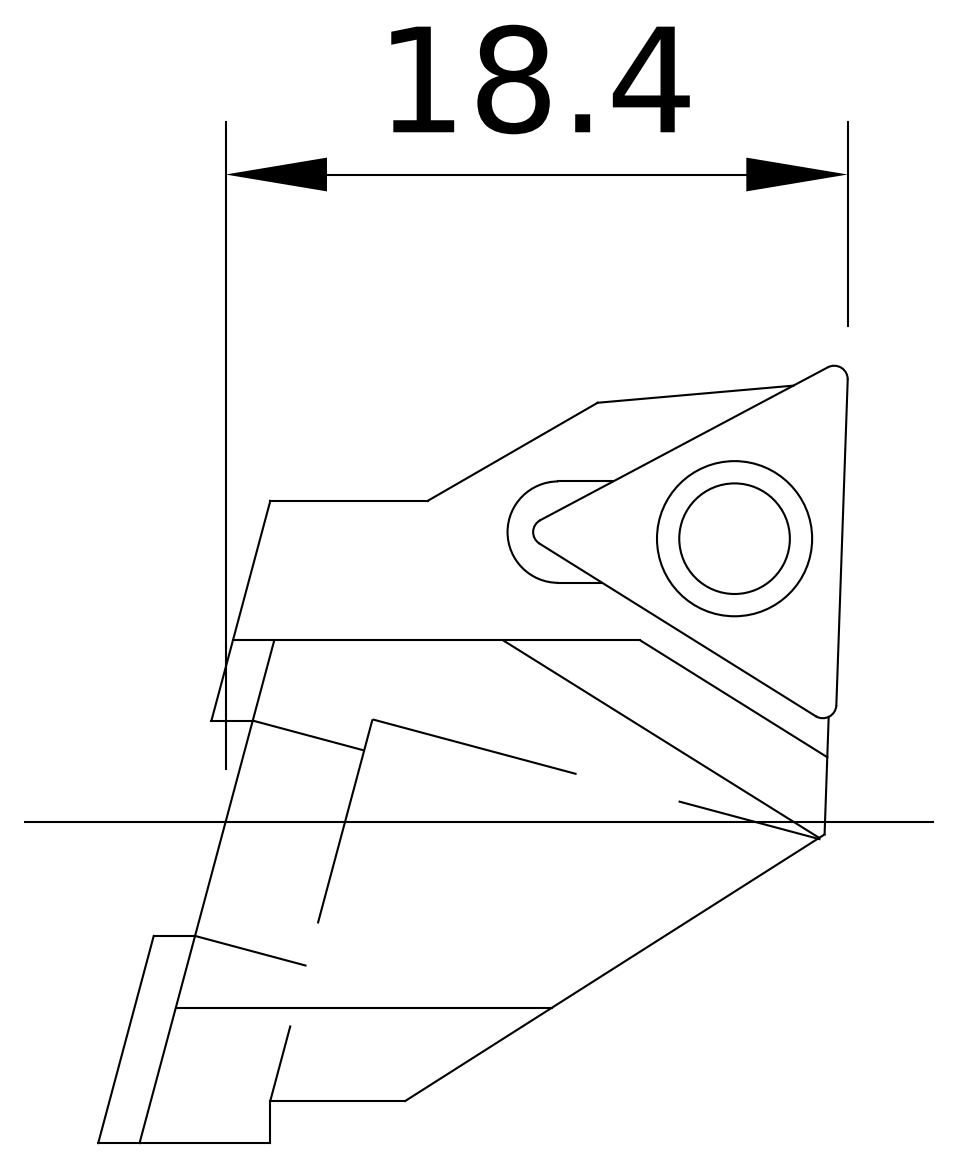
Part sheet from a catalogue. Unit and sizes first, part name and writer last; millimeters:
Units: millimetres
Overall size (bounding box): 24.5 × 22.26 × 12.9
Round holes (diameter × count): ⌀2 ×1, ⌀2.8 ×1
Round bosses / shafts (diameter × count): ⌀3.45 ×1, ⌀2.5 ×1
Partial cylindrical surfaces — rounded edges, fillets, slot ends (radius × count): R0.15 ×6, R0.4 ×6, R2.6 ×2, R1.6 ×1, R4.4 ×1, R9.55 ×1, R14.03 ×1
Main face-to-face distances: 12.9, 6.45, 4.35, 8.55, 6.73, 2.38, 6.17, 2.05, 10.85, 4.4
Volume: 2 354 mm³ · Surface area: 2 334 mm²
Bodies: 5 solids, 142 faces (51 planar, 41 cylindrical, 50 other)
Part name (STEP PRODUCT): 615.303 Kaiser E27_33 TC11|694.122 Kaiser ETL M2.5x6.5 T7 IP 10S;Kreismuster1; 615.303 Kaiser E27_33 TC11|655.383 Kaiser TCGT 110204 K10C;Kombinieren1; 615.303 Kaiser E27_33 TC11|615.303 Kaiser E27_33 TC11-2;Verrundung1; 615.303 Kaiser E27_33 TC11|615.303 Kaiser E27_33 TC11-1;<N016.05 (TC 1102) PLS rechts Freistellung neutral>-<<655.321>-<Kombinieren1>> (+1 more)
STEP written by: ACIS (automotive_design)
